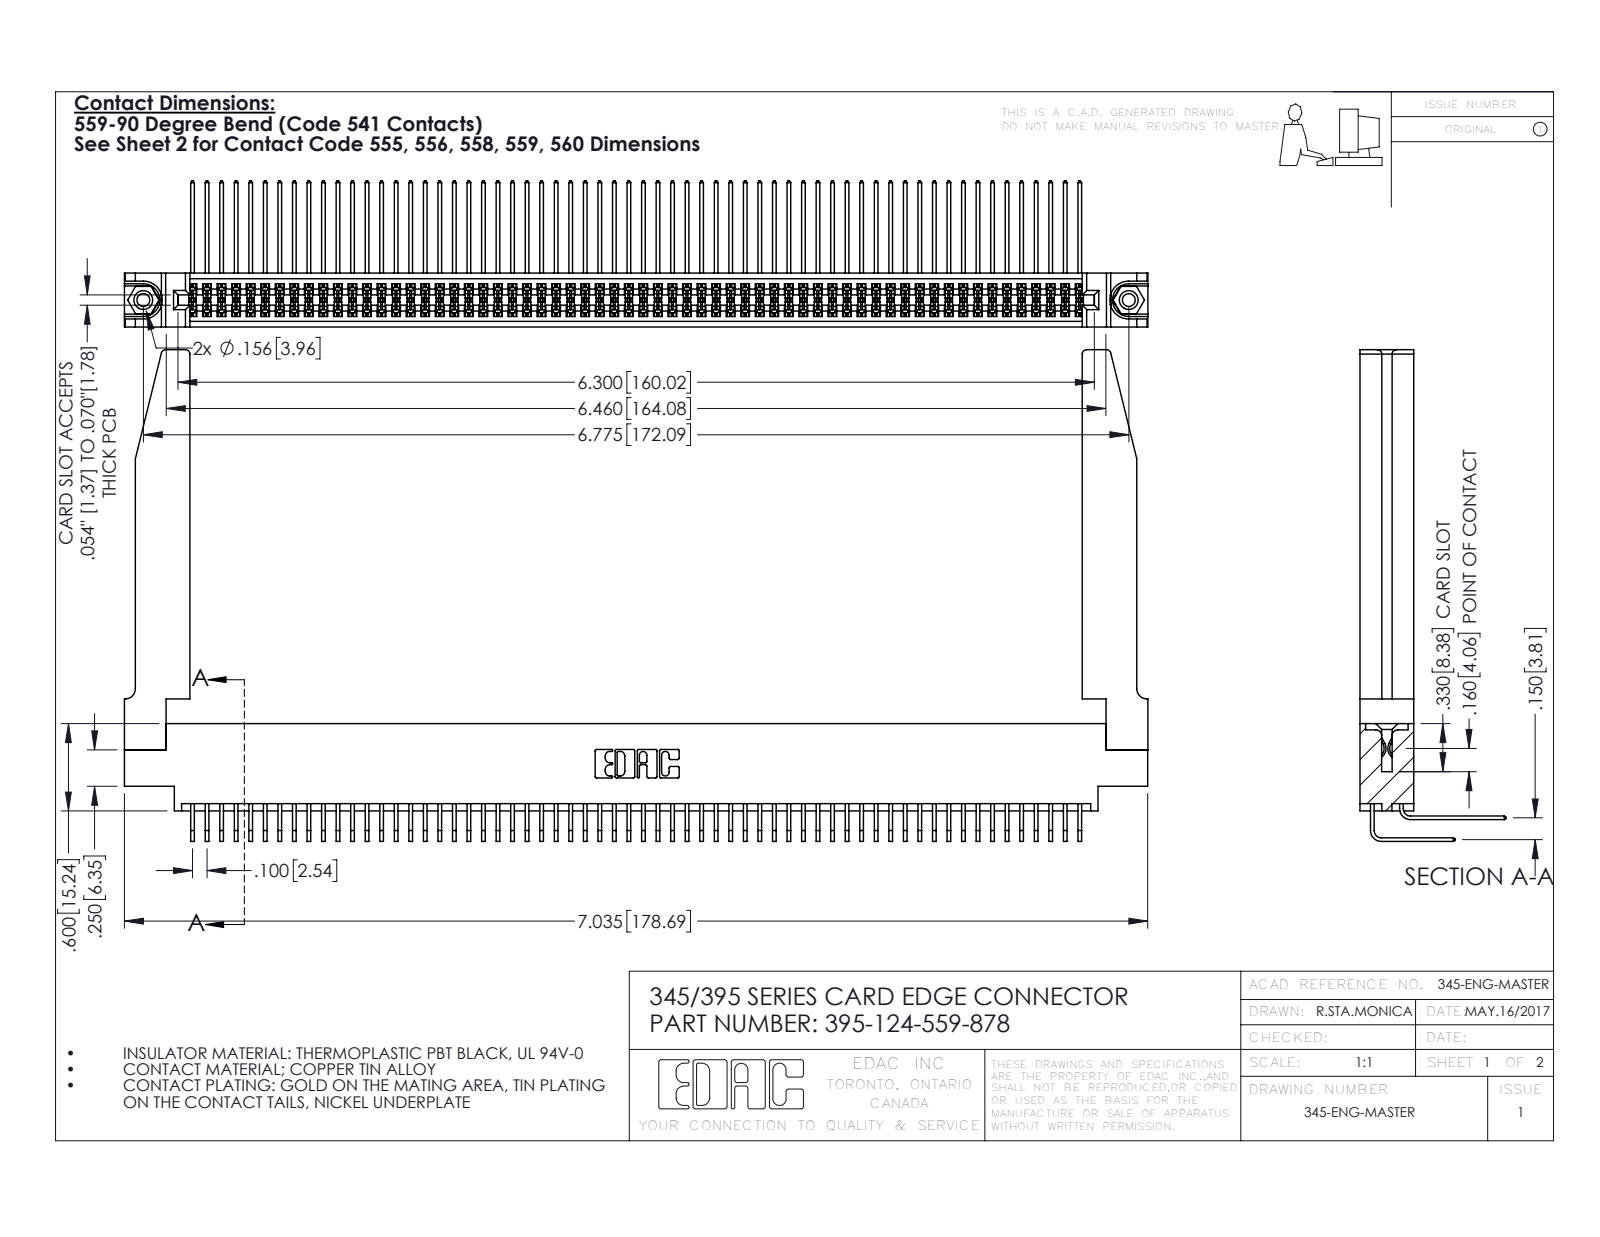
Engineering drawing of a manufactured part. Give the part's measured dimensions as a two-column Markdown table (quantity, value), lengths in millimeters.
| quantity | value |
| --- | --- |
| part name | 345 Part_0.170 Offset - 0.156 Dia-TH; 345-220-078_345-220-078; 345-292-001_558 559 Tail - 1; 345-250-001_345-250-001-102 (+2 more) |
| STEP written by | SolidWorks 2016 (CONFIG_CONTROL_DESIGN) |
| units | millimeters |
| bodies | 129 solids, 6812 faces (4566 planar, 2194 cylindrical, 52 other) |
| overall size | 178.7 × 85.8 × 25.5 |
| volume | 25 920 mm³ |
| surface area | 37 560 mm² |
| round holes (diameter × count) | 2.3 × 2, 3.2 × 2, 4 × 2, 1.6 × 1 |
| round bosses / shafts (diameter × count) | 3.9 × 2 |
| partial cylindrical surfaces (radius × count) | 0.2 × 186, 0.3 × 22, 0.8 × 8, 0.2 × 6, 0.8 × 6, 0.7 × 3, 0.4 × 2, 0.5 × 2 |
| main face-to-face distances | 1.8, 7.6, 9.4, 2.5, 6.9, 0.6, 5.1, 5.7, 3.8, 4.4 |
| hole center spacings | 6.9, 166.1, 172.1 |
